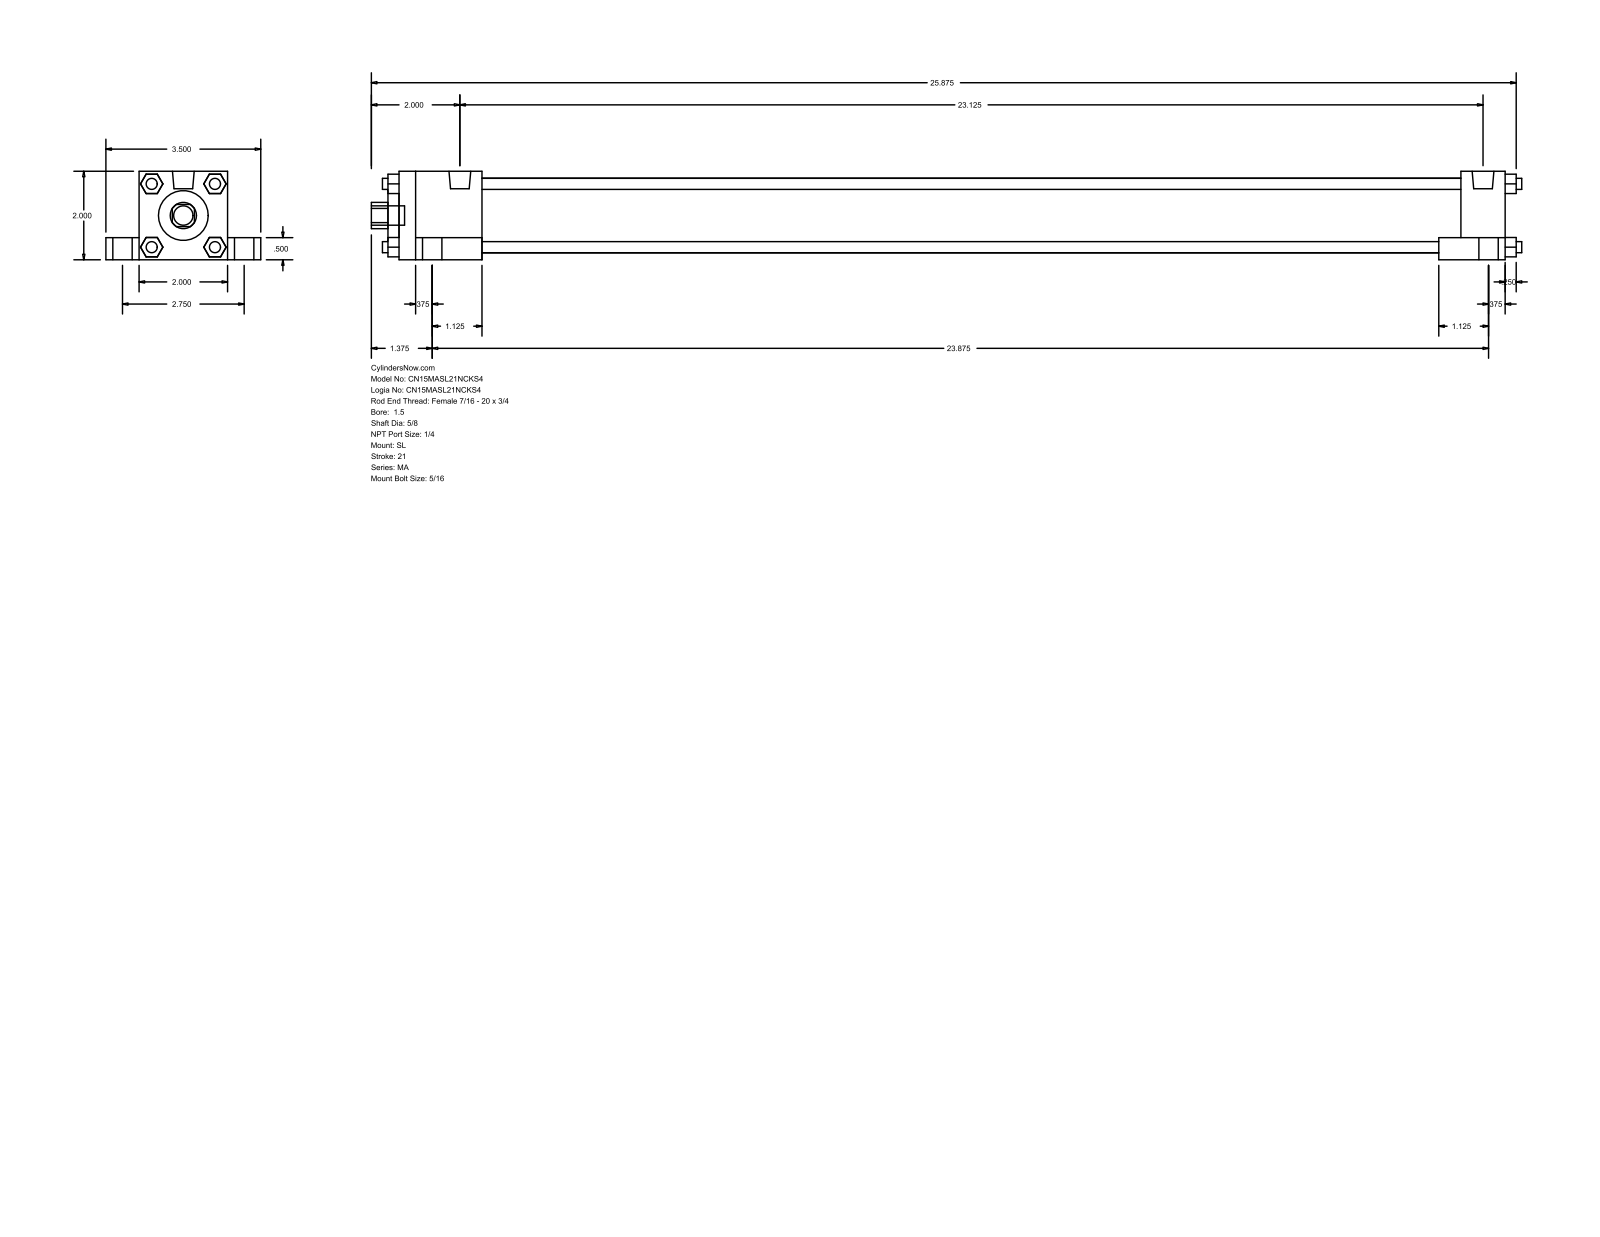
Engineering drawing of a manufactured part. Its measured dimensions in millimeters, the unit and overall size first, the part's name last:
Units: millimetres
Overall size (bounding box): 660.4 × 88.9 × 50.8
Round holes (diameter × count): ⌀15.88 ×1, ⌀28.57 ×1, ⌀42.93 ×1
Round bosses / shafts (diameter × count): ⌀11.11 ×5, ⌀17.46 ×4, ⌀7.94 ×4, ⌀6.35 ×4, ⌀12.49 ×2
Partial cylindrical surfaces — rounded edges, fillets, slot ends (radius × count): R7.54 ×1
Main face-to-face distances: 50.8, 19.05, 38.1, 12.7, 635, 69.85, 9.52, 6.35, 641.35, 25.4
Bodies: 0 solids, 148 faces (112 planar, 36 cylindrical, 0 other)
Part name (STEP PRODUCT): MA_SL__0150_0.625
STEP written by: GSSL Pune (CONFIG_CONTROL_DESIGN)
